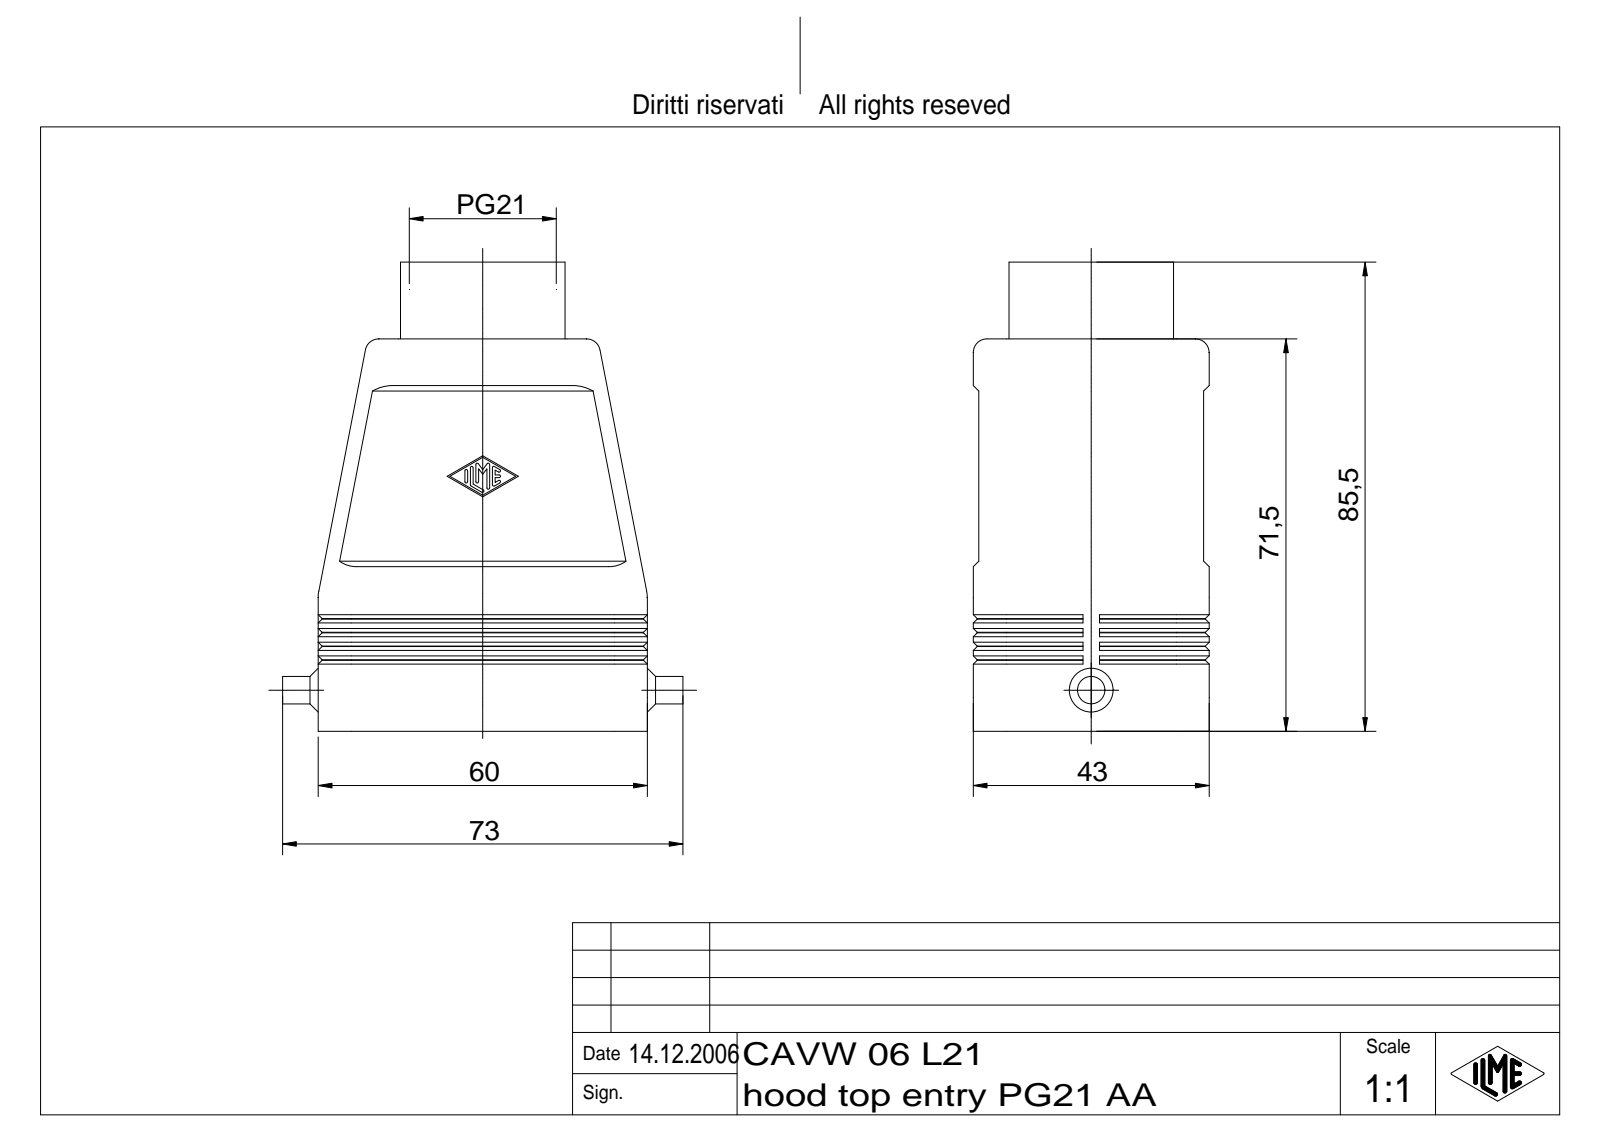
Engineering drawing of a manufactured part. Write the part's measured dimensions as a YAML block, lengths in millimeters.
part_name: "CAV Tüllengehäuse 1 Bügel für einen Einsatz"
step_written_by: "Autodesk Inventor 7 (AUTOMOTIVE_DESIGN)"
units: millimeters
bodies: {solids: 1, faces: 397, planar: 152, cylindrical: 104, other: 141}
overall_size: [85.5, 73, 43]
volume: 56512
surface_area: 30889
round_holes:
  - {diameter: 24.78, count: 1}
  - {diameter: 26.78, count: 1}
round_bosses_or_shafts:
  - {diameter: 30, count: 1}
  - {diameter: 25.78, count: 1}
  - {diameter: 5, count: 1}
partial_cylinders:
  - {radius: 0.25, count: 14}
  - {radius: 6, count: 10}
  - {radius: 2, count: 4}
  - {radius: 2.5, count: 4}
  - {radius: 3, count: 4}
  - {radius: 5.3, count: 2}
face_to_face_distances: [4, 38, 3, 1, 39, 42, 35, 7, 11, 41]
